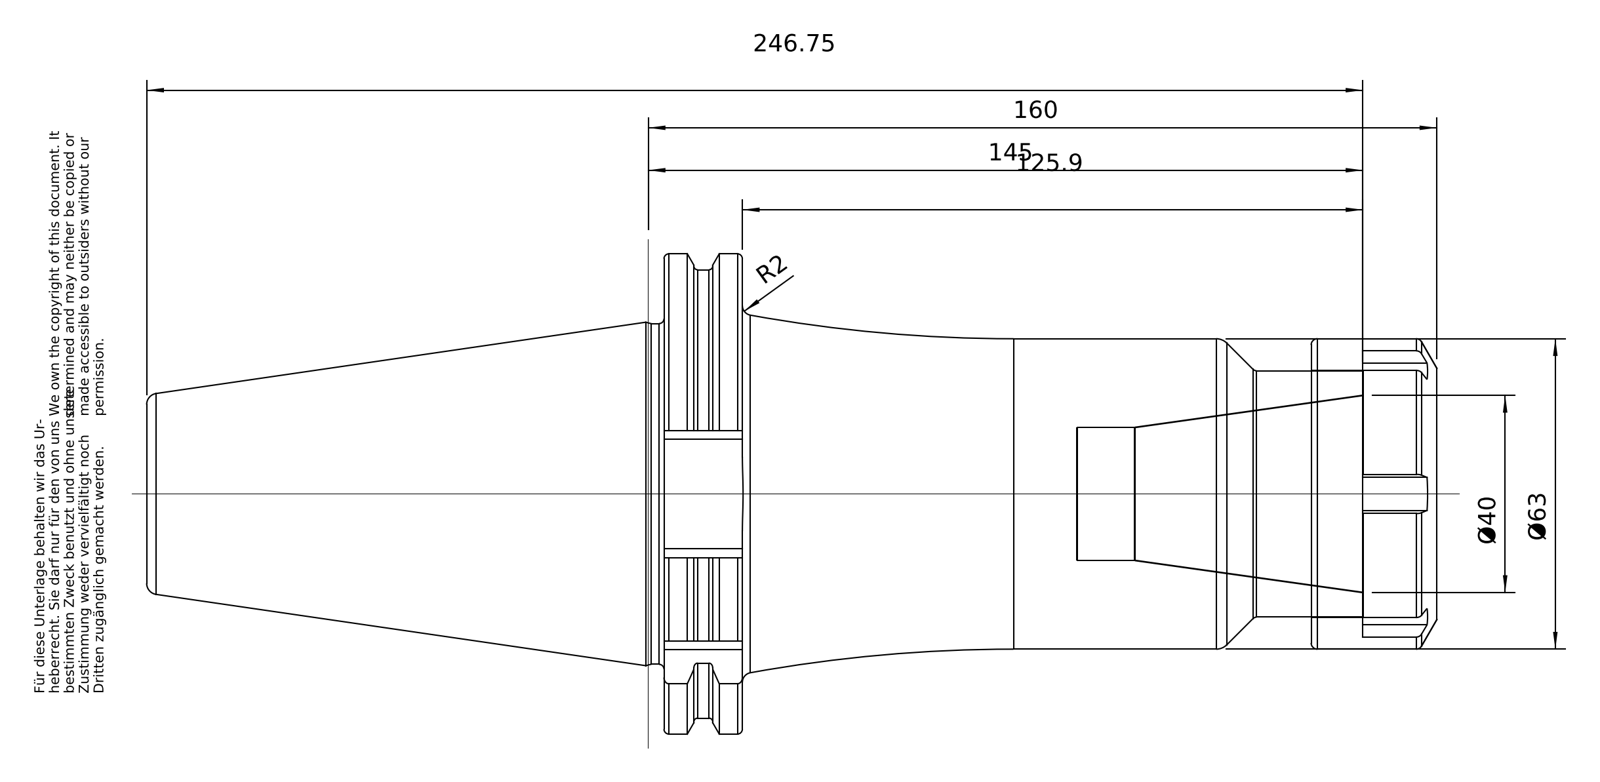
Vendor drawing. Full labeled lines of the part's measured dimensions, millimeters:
Part name (STEP PRODUCT): 50-322-40; 83-912-40; 50-322-40_ASM
STEP written by: PRO/ENGINEER BY PARAMETRIC TECHNOLOGY CORPORATION, 2010430 (CONFIG_CONTROL_DESIGN)
Units: millimetres
Bodies: 2 solids, 152 faces (51 planar, 38 cylindrical, 63 other)
Overall size (bounding box): 261.6 × 97.47 × 94
Volume: 749 923 mm³ · Surface area: 81 430 mm²
Round holes (diameter × count): ⌀20.75 ×1, ⌀25.01 ×1, ⌀25.7 ×1, ⌀27 ×1
Round bosses / shafts (diameter × count): ⌀91 ×1, ⌀69.15 ×1, ⌀63 ×1, ⌀50 ×1, ⌀24.01 ×1
Partial cylindrical surfaces — rounded edges, fillets, slot ends (radius × count): R2.7 ×6, R1.75 ×5, R48.74 ×1
Main face-to-face distances: 131.3, 15.85, 115.45, 156.8, 140.95, 25.5, 141.8, 125.95, 10.5, 15
